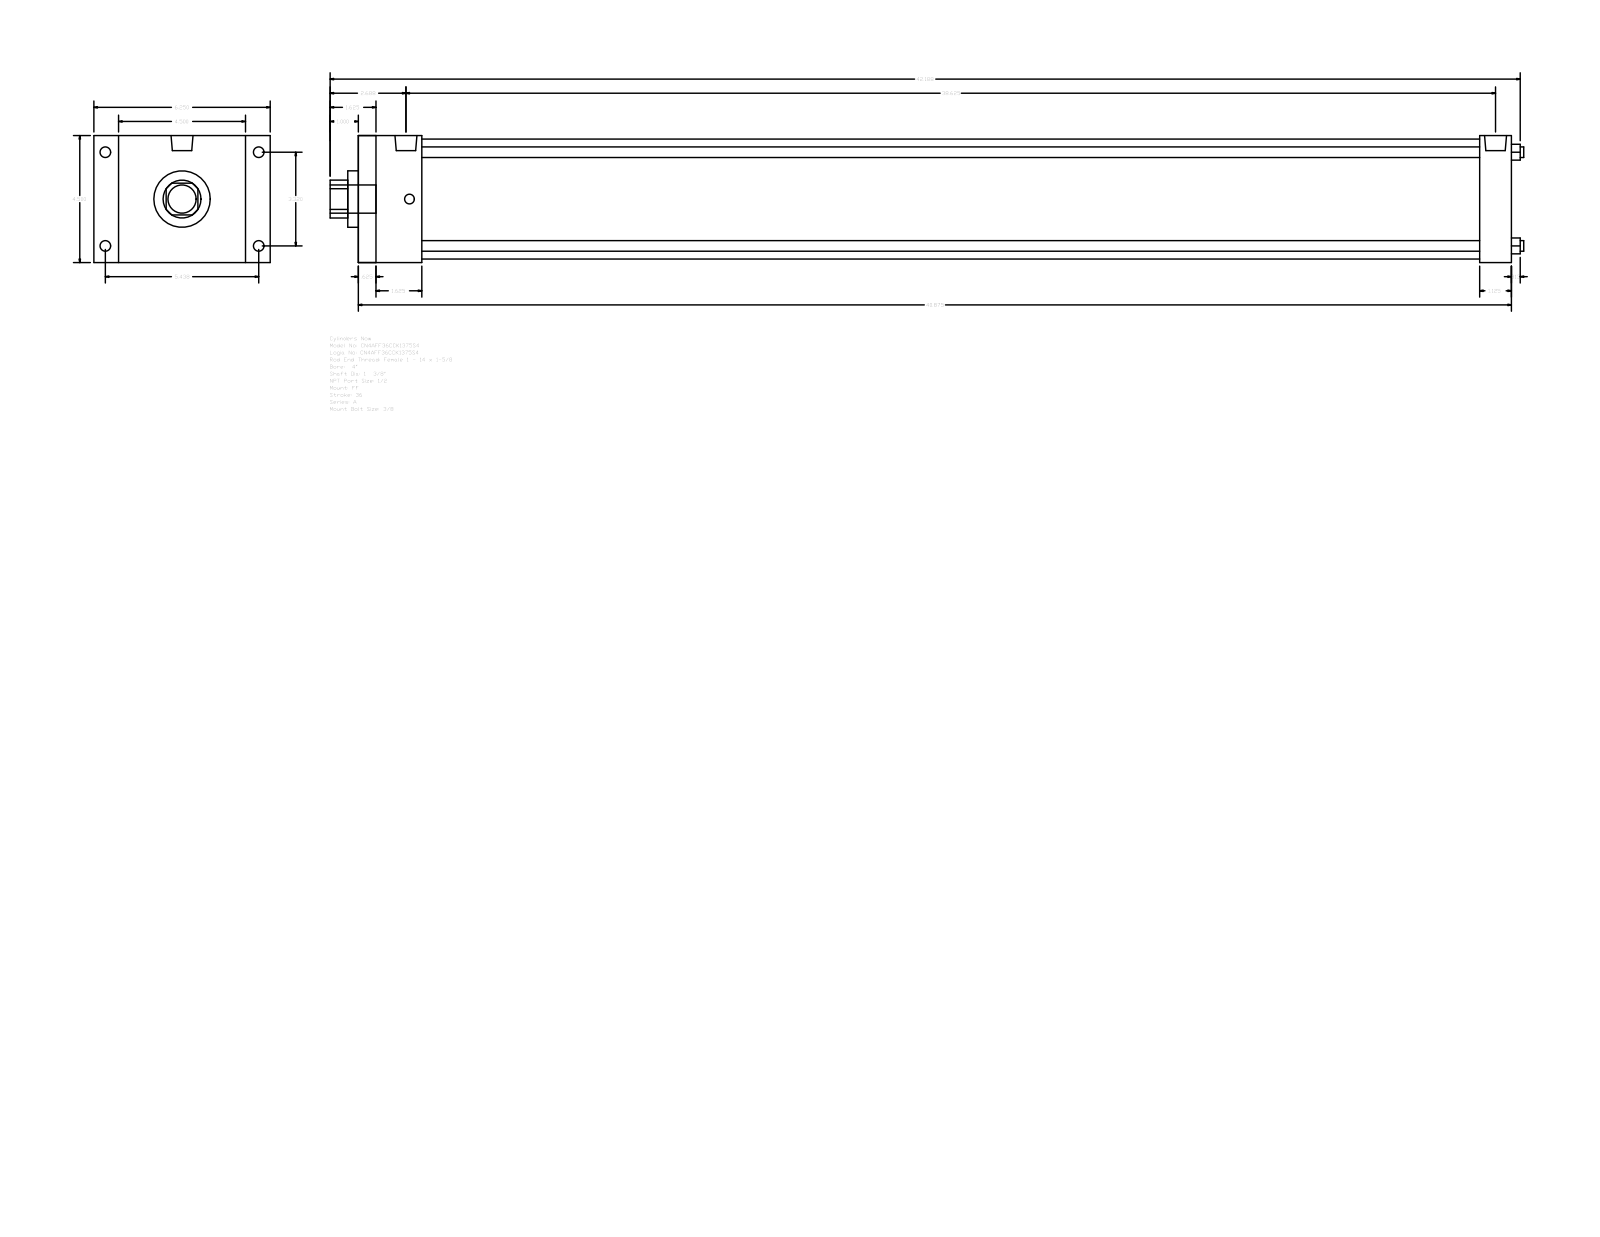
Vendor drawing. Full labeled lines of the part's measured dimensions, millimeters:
Part name (STEP PRODUCT): A_FF__0400_1.375
STEP written by: GSSL Pune (CONFIG_CONTROL_DESIGN)
Units: millimetres
Bodies: 0 solids, 92 faces (64 planar, 28 cylindrical, 0 other)
Overall size (bounding box): 1074.74 × 158.75 × 114.3
Round holes (diameter × count): ⌀9.53 ×4, ⌀34.92 ×1, ⌀50.8 ×1, ⌀107.95 ×1
Round bosses / shafts (diameter × count): ⌀9.53 ×4, ⌀8.73 ×4, ⌀19.77 ×2, ⌀25.4 ×1
Partial cylindrical surfaces — rounded edges, fillets, slot ends (radius × count): R17.06 ×1
Main face-to-face distances: 114.3, 1038.22, 1022.35, 15.87, 28.57, 22.23, 136.53, 1009.65, 993.78, 57.15
Hole centre spacings: 59.62, 84.32, 119.25
